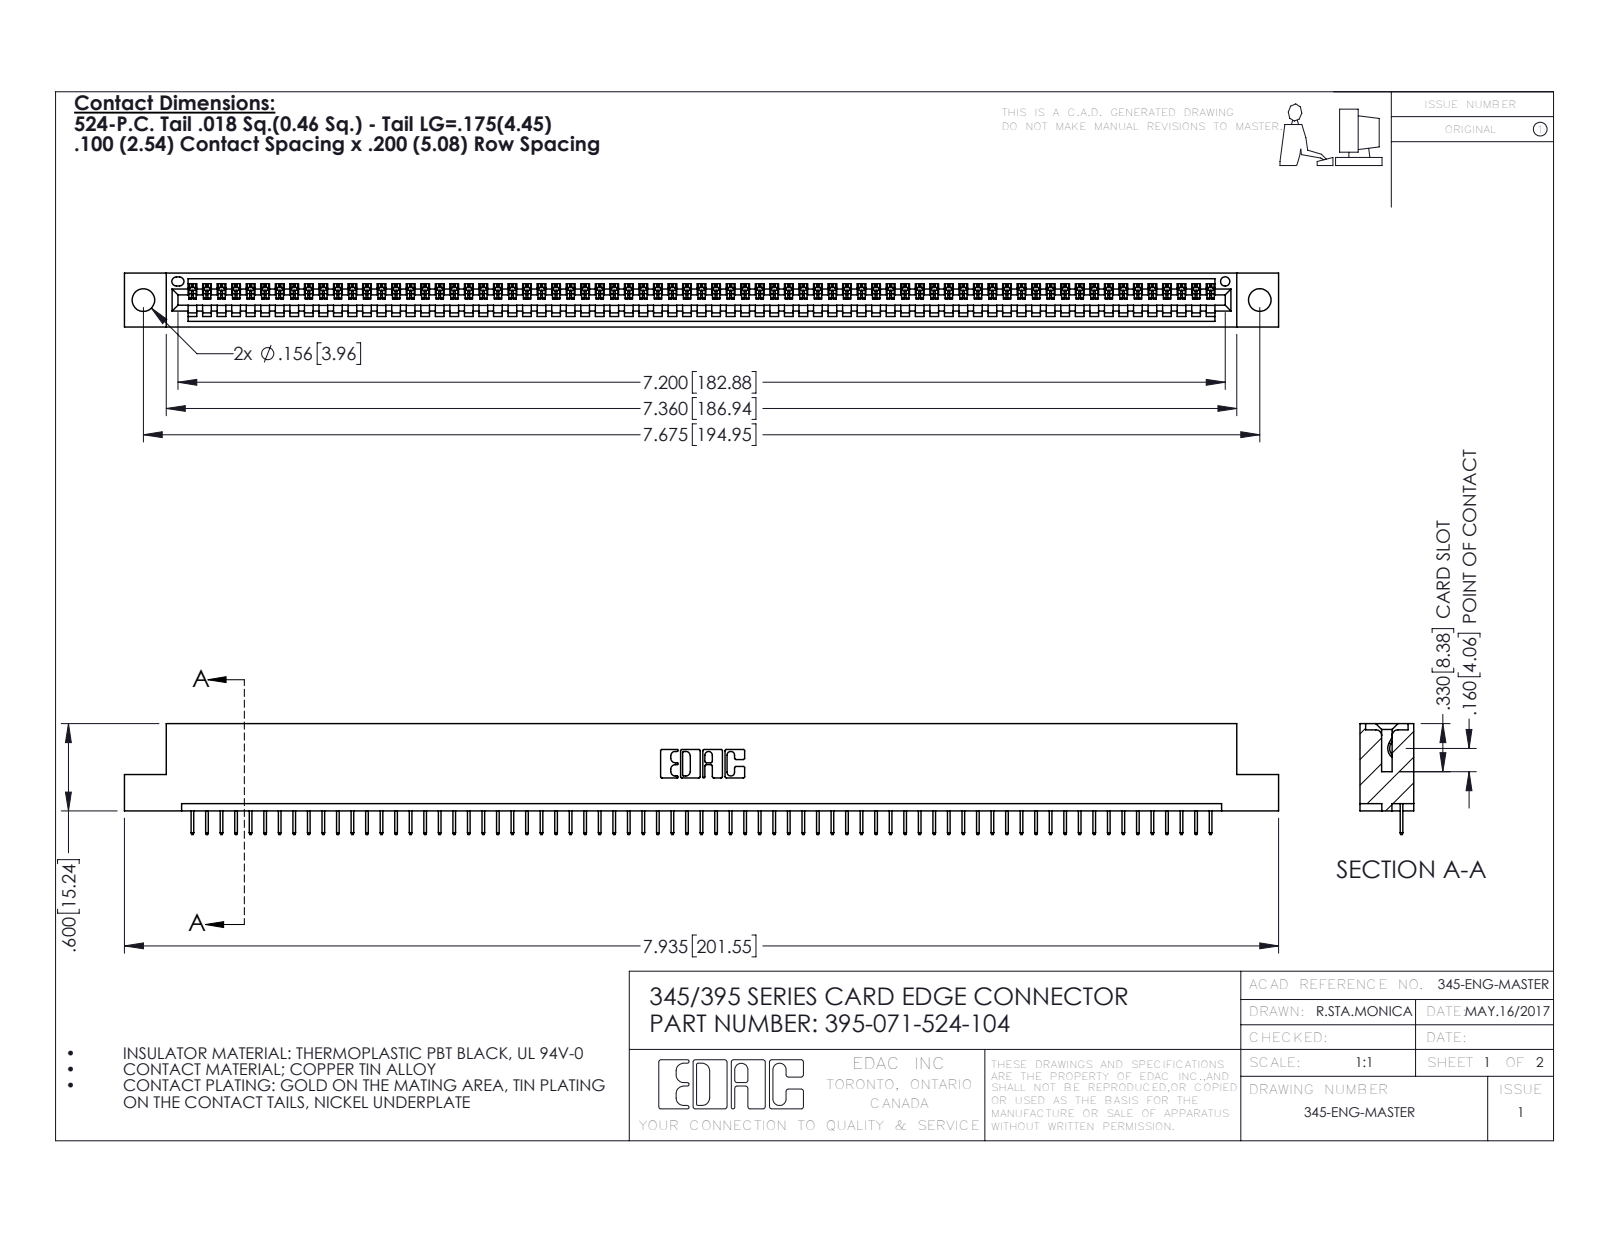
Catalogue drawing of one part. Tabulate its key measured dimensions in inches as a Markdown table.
| quantity | value |
| --- | --- |
| part name | 395-071-524-104; 345-292-001_345-293-124; 345 Part_Flush Mounting Lugs - 0.156 Dia-TH |
| STEP written by | SolidWorks 2016 (CONFIG_CONTROL_DESIGN) |
| units | inches |
| bodies | 72 solids, 4528 faces (3346 planar, 1182 cylindrical, 0 other) |
| overall size | 7.935 × 0.762 × 0.37 |
| volume | 1.16 in³ |
| surface area | 38.09 in² |
| round holes (diameter × count) | 0.156 × 2, 0.064 × 1 |
| partial cylindrical surfaces (radius × count) | 0.006 × 142, 0.01 × 22, 0.007 × 6, 0.031 × 6, 0.026 × 3, 0.031 × 2, 0.04 × 2, 0.014 × 1 |
| main face-to-face distances | 0.298, 0.072, 0.37, 0.2, 0.098, 0.272, 0.025, 0.225, 0.072, 0.149 |
| hole center spacings | 0.27, 7.439, 7.675 |
